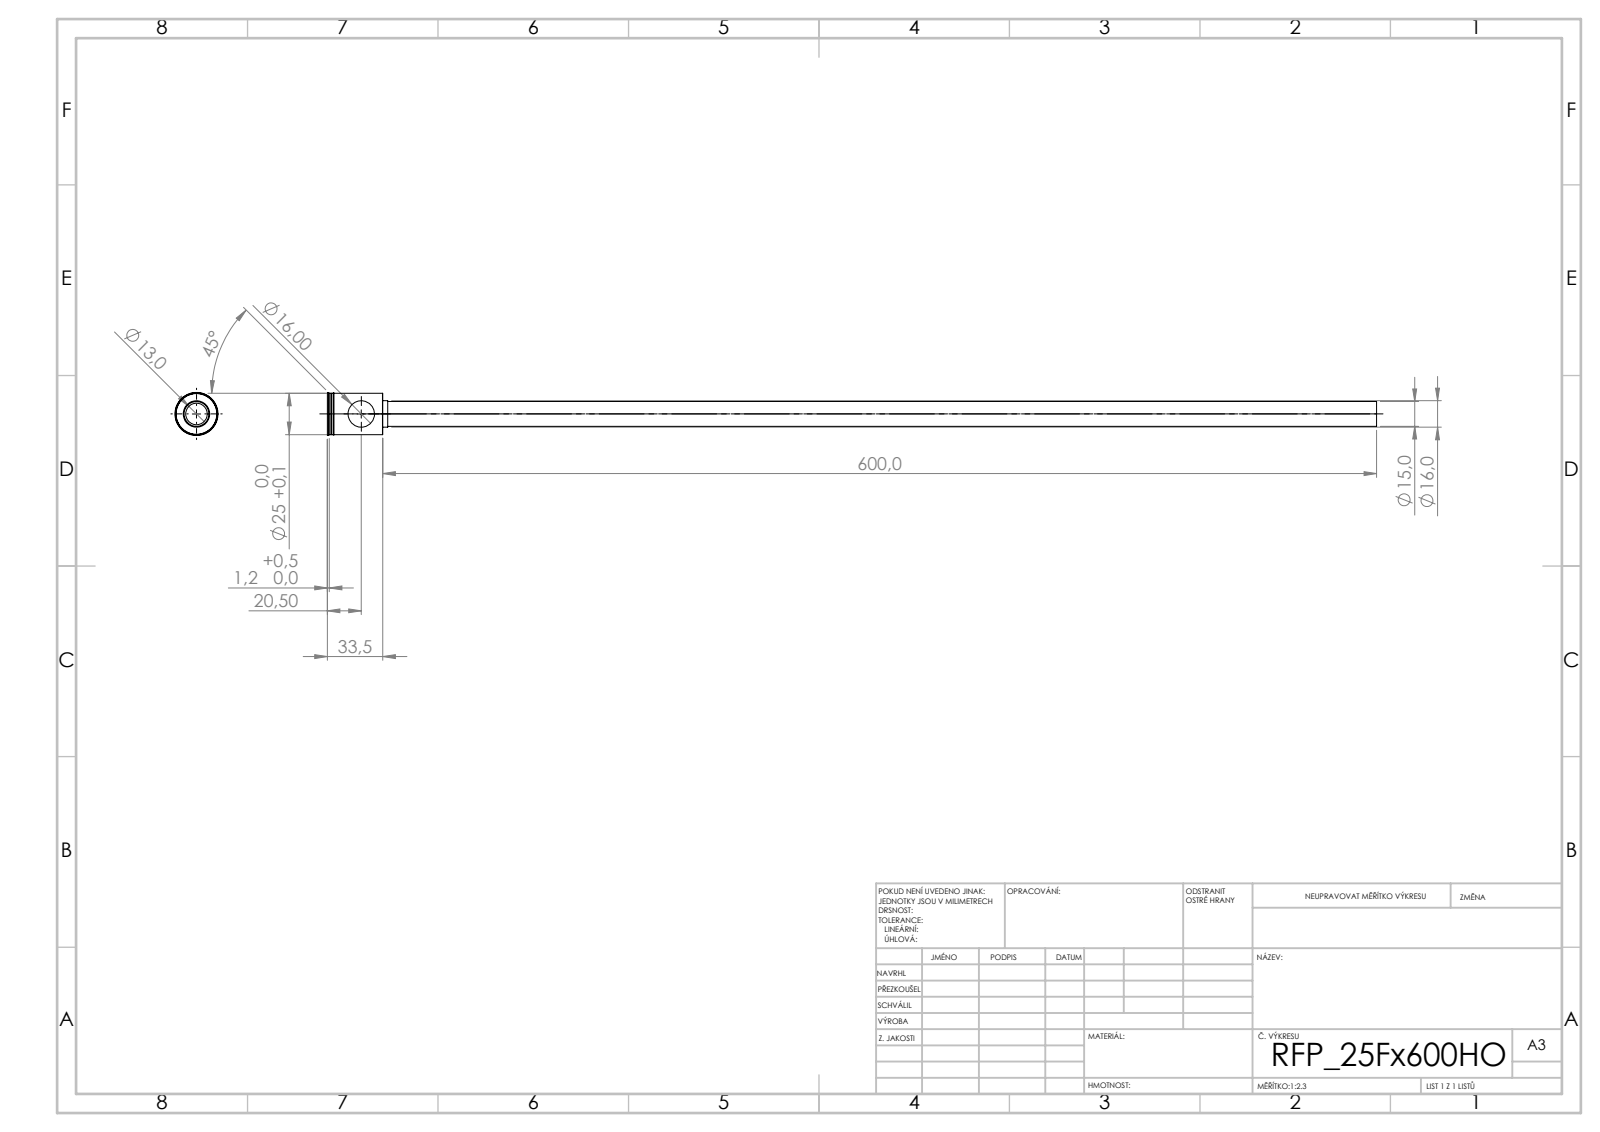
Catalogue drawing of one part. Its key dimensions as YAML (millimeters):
step_written_by: "SolidWorks 2019 (CONFIG_CONTROL_DESIGN)"
units: millimeters
bodies: {solids: 1, faces: 44, planar: 20, cylindrical: 16, other: 8}
overall_size: [633.5, 26, 26]
volume: 36712
surface_area: 57325
round_holes:
  - {diameter: 13, count: 1}
  - {diameter: 16, count: 1}
round_bosses_or_shafts:
  - {diameter: 26, count: 1}
  - {diameter: 25, count: 1}
  - {diameter: 16, count: 1}
  - {diameter: 15, count: 1}
face_to_face_distances: [31.5, 2, 33.5, 20.4, 600, 631.5, 633.5, 0.5, 597, 3]
